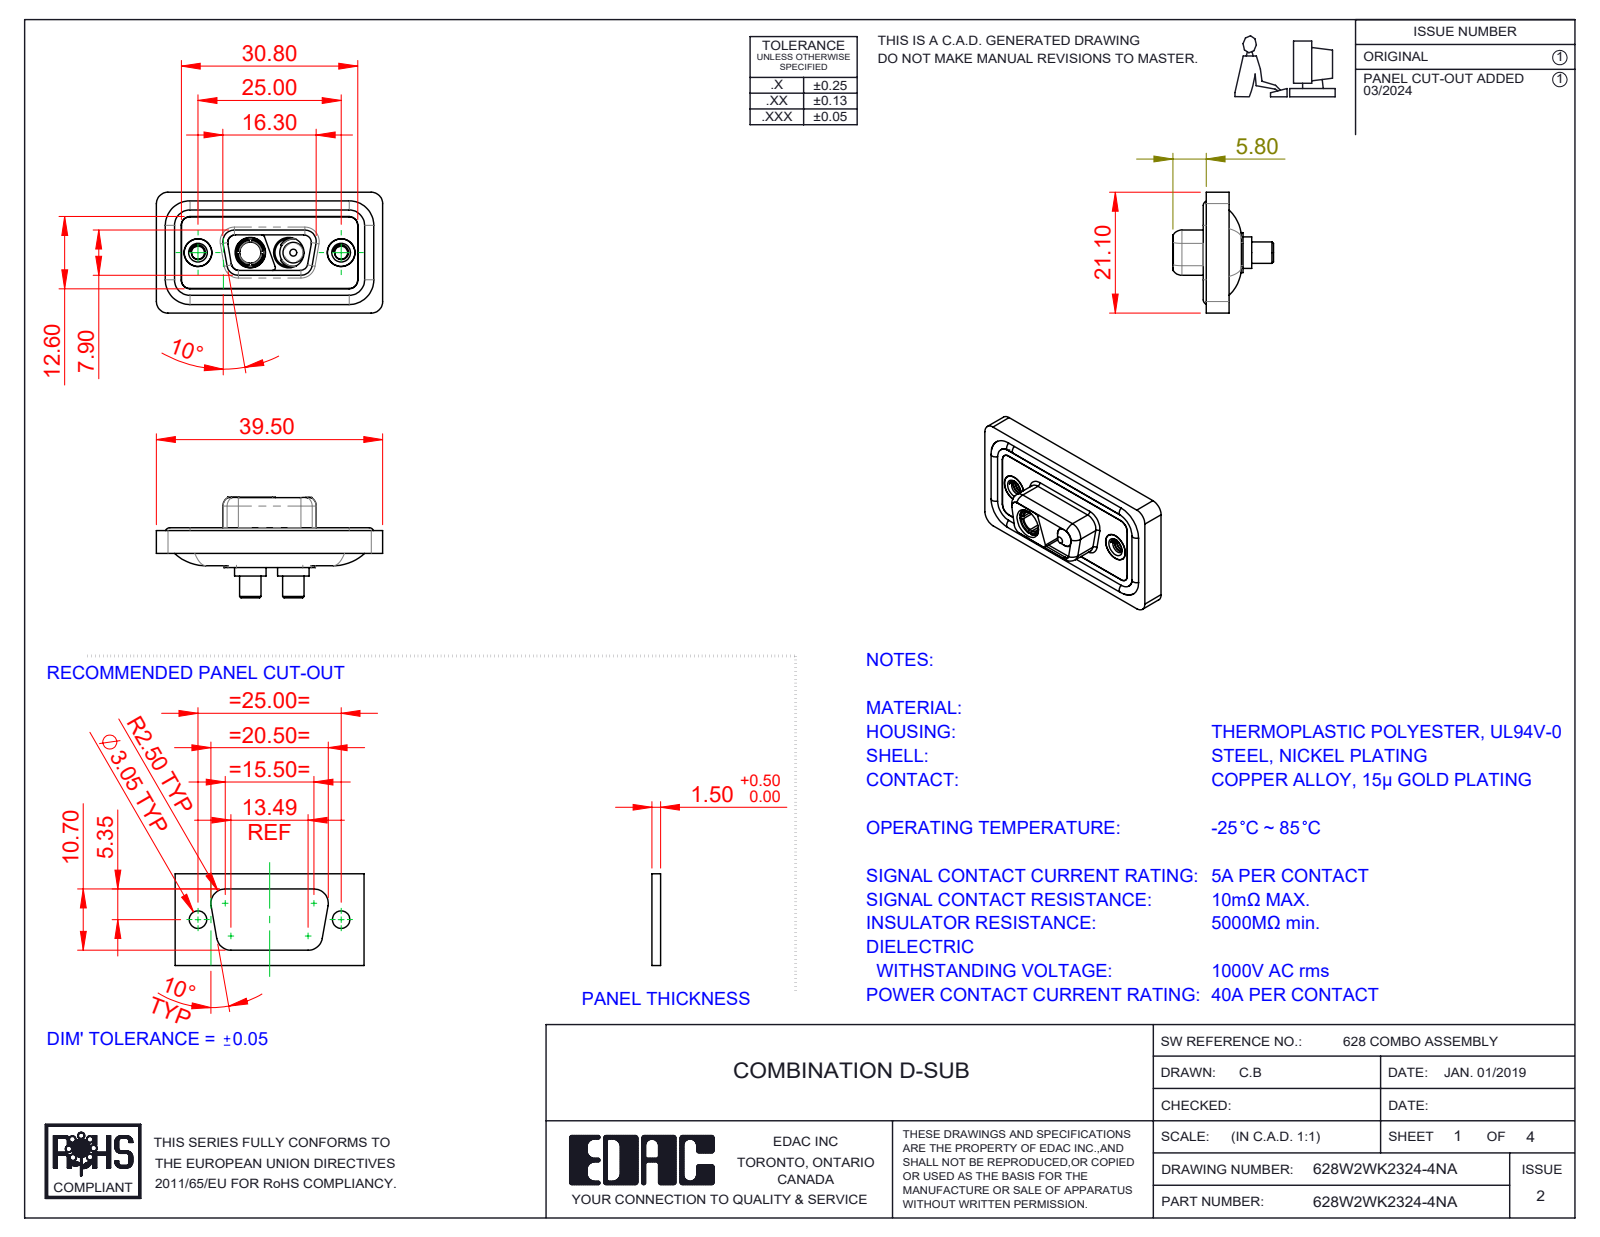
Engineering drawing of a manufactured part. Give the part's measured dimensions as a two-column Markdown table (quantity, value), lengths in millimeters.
| quantity | value |
| --- | --- |
| part name | 628Combo Waterproof Housing_09 Contacts; Power Pin_40A S; 628W2WK2324-4NA; 628Combo Shell Front_09 Contacts (+4 more) |
| STEP written by | SolidWorks 2023 (CONFIG_CONTROL_DESIGN) |
| units | millimeters |
| bodies | 11 solids, 498 faces (144 planar, 233 cylindrical, 121 other) |
| overall size | 39.5 × 21.1 × 17.55 |
| volume | 4 642 mm³ |
| surface area | 7 363 mm² |
| round holes (diameter × count) | 4.85 × 4, 2.26 × 2, 4 × 2, 4.05 × 2, 5 × 2, 5.3 × 2, 3.7 × 1 |
| round bosses / shafts (diameter × count) | 1.6 × 4, 5.5 × 2, 5.2 × 2, 4.95 × 2, 4.8 × 2, 4.75 × 2, 3.75 × 2, 4.96 × 1 |
| partial cylindrical surfaces (radius × count) | 1.5 × 22, 2 × 18, 1.35 × 8, 1.6 × 8, 0.5 × 6, 0.25 × 4, 0.6 × 4, 0.65 × 4 |
| main face-to-face distances | 0.4, 1.1, 2.9, 1.6, 0.5, 1.8, 5.65, 5.35, 3.1, 1.5 |
| hole center spacings | 9.14, 15.86, 6.72, 25 |
